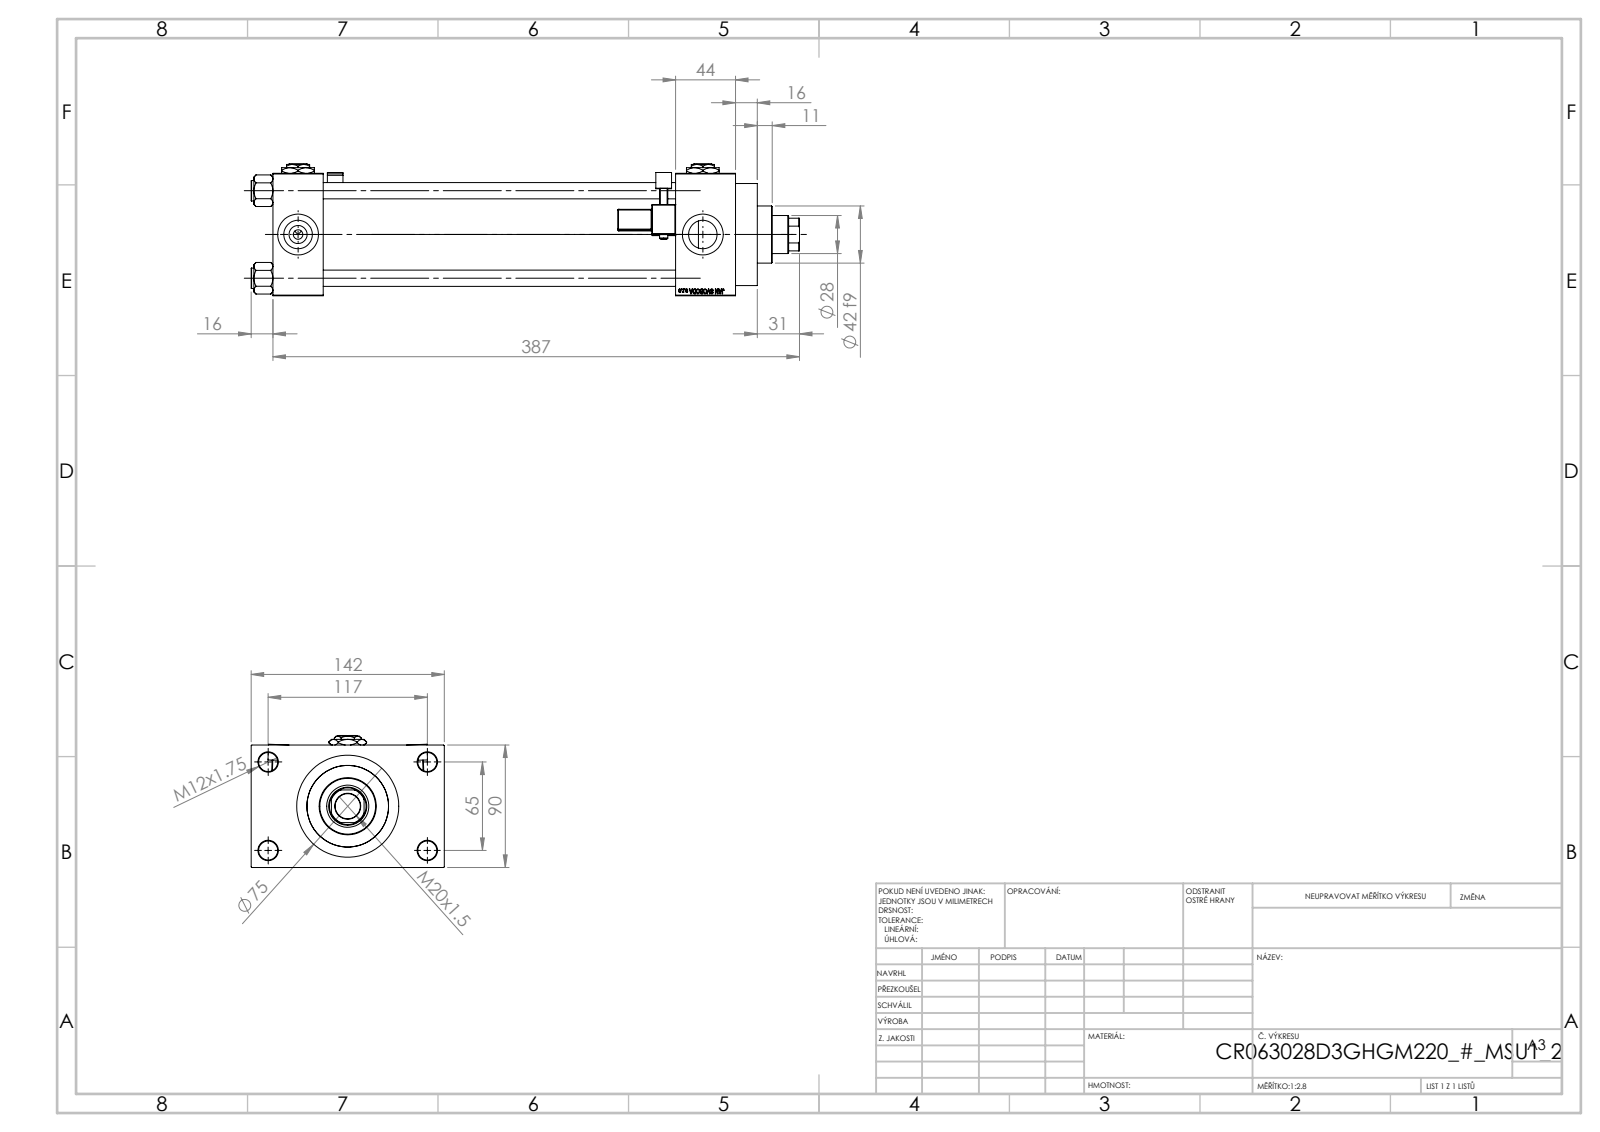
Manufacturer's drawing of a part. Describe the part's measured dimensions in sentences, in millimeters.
The part is named "NUT_M5_D; Zatka_pro_OIL_PORT; V215CR_D_TYCINKA; V215_VC_A (+3 more)". Its 3-D file was written by "SolidWorks 2019 (CONFIG_CONTROL_DESIGN)". It is 15 solids with 1358 faces: 603 planar, 159 cylindrical and 596 other. Overall it measures 403 by 142 by 97 millimeters. Its volume is 1 470 000 cubic millimeters and its surface area 347 901 square millimeters. Round holes: 4 of diameter 12, 4 of diameter 14, 4 of diameter 20.96, 4 of diameter 30, 3 of diameter 7, 1 of diameter 18.5, 1 of diameter 28, 1 of diameter 31, 1 of diameter 50, 1 of diameter 60, 1 of diameter 63. Round bosses or shafts: 4 of diameter 15, 2 of diameter 6, 1 of diameter 75, 1 of diameter 69, 1 of diameter 42. Partial cylindrical surfaces (rounded edges, fillets, slot ends): 48 of radius 0.5, 2 of radius 1, 2 of radius 2.5, 2 of radius 4, 1 of radius 13.5. The main face-to-face distances are 90, 259, 37, 296, 340, 303, 44, 26, 116, 16. The hole center spacings are 26.35, 45.47, 64.3, 66.92, 69.81, 90.65, 111.34, 65.
